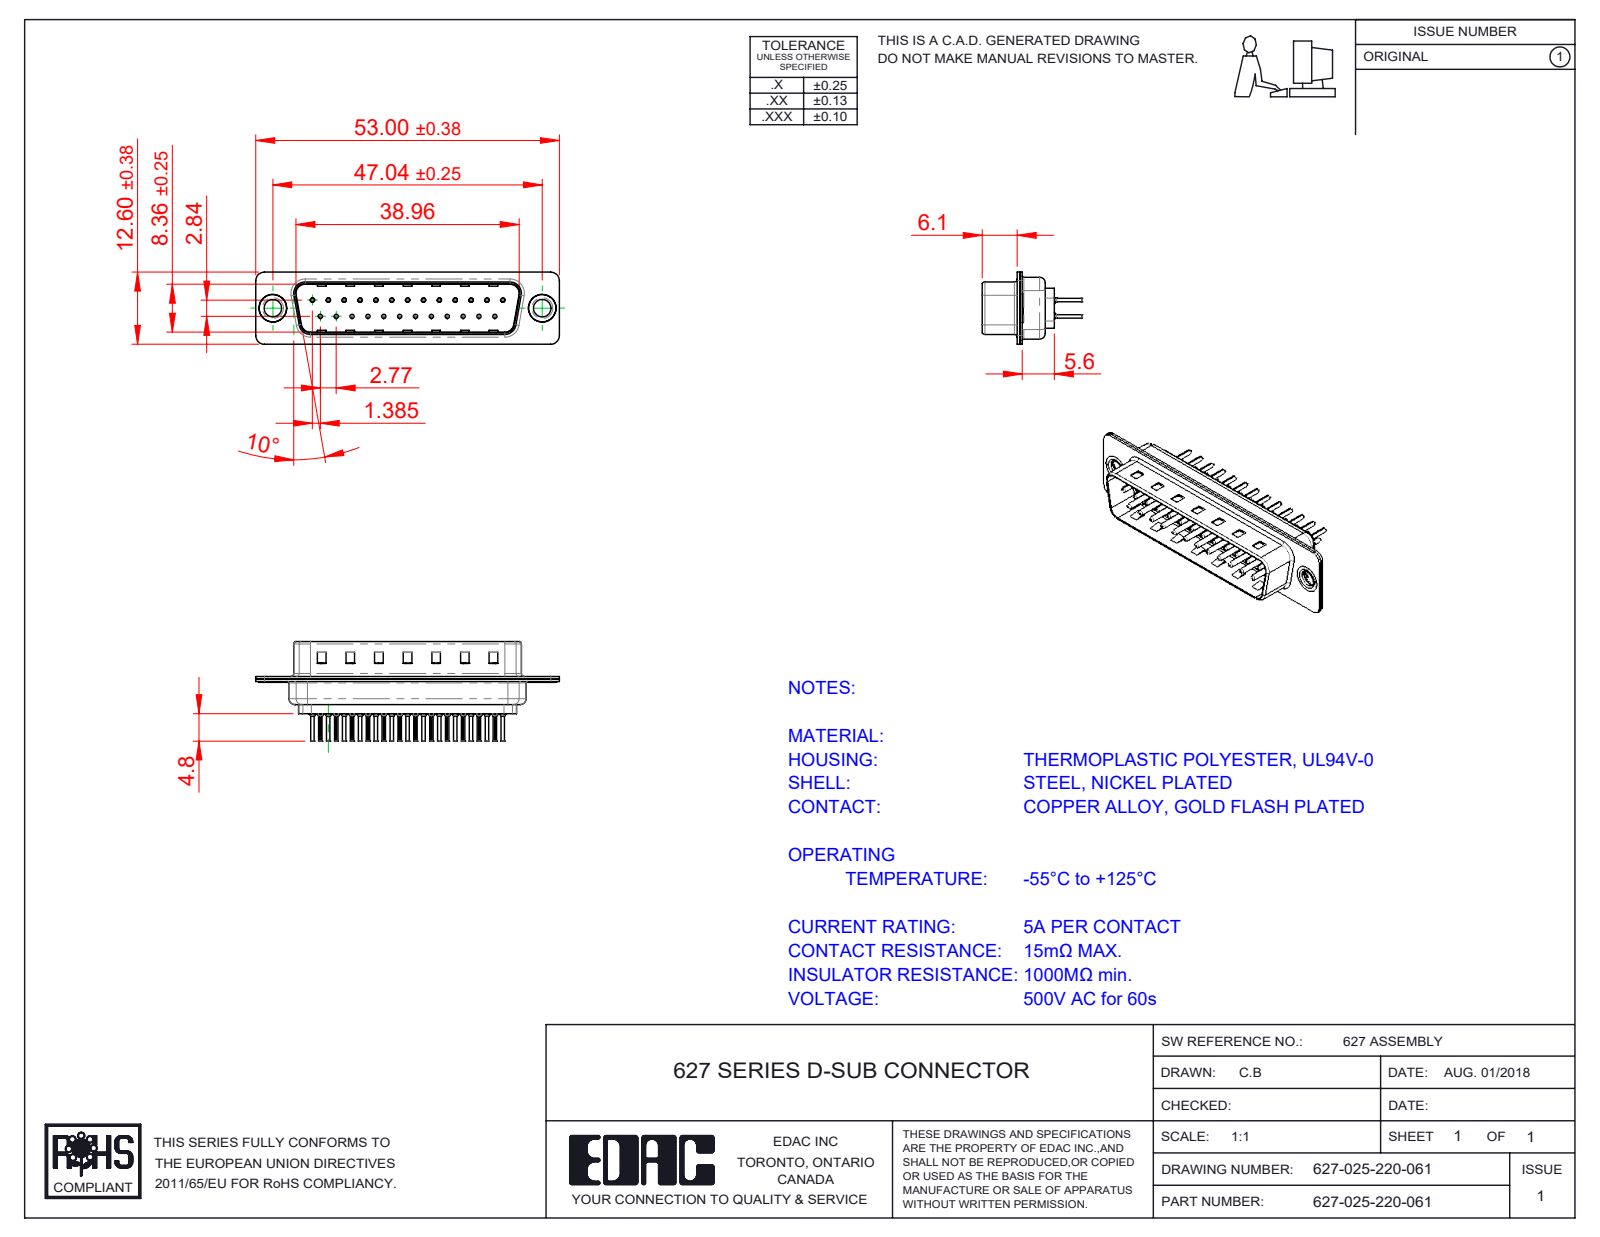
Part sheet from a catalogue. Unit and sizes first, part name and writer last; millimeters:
Units: millimetres
Overall size (bounding box): 53 × 17.3 × 12.6
Round holes (diameter × count): ⌀0.2 ×25, ⌀0.35 ×25, ⌀1.1 ×25, ⌀1.6 ×25, ⌀3.05 ×2, ⌀4 ×2, ⌀4.8 ×2
Round bosses / shafts (diameter × count): ⌀2 ×25, ⌀1.5 ×25, ⌀0.75 ×25, ⌀0.6 ×25, ⌀5 ×2, ⌀4.9 ×2, ⌀3.55 ×2
Partial cylindrical surfaces — rounded edges, fillets, slot ends (radius × count): R0.1 ×50, R1.5 ×16, R2 ×12, R0.5 ×8, R1.6 ×8, R0.25 ×4, R0.6 ×4, R0.65 ×4
Main face-to-face distances: 0.4, 0.45, 0.82, 9.58, 0.9, 8.76, 1.5, 1.4, 6.5, 6.05
Hole centre spacings: 3.16, 8.31, 2.77, 5.54, 11.08, 16.62, 5.03, 5.04
Volume: 2 604 mm³ · Surface area: 7 660 mm²
Bodies: 30 solids, 2800 faces (771 planar, 1046 cylindrical, 983 other)
Part name (STEP PRODUCT): 627 Housing_25 LP; 627 Thru Hole Rivet; 627-025-220-061; 627 Contact Row 2_20L (+3 more)
STEP written by: SolidWorks 2020 (CONFIG_CONTROL_DESIGN)
